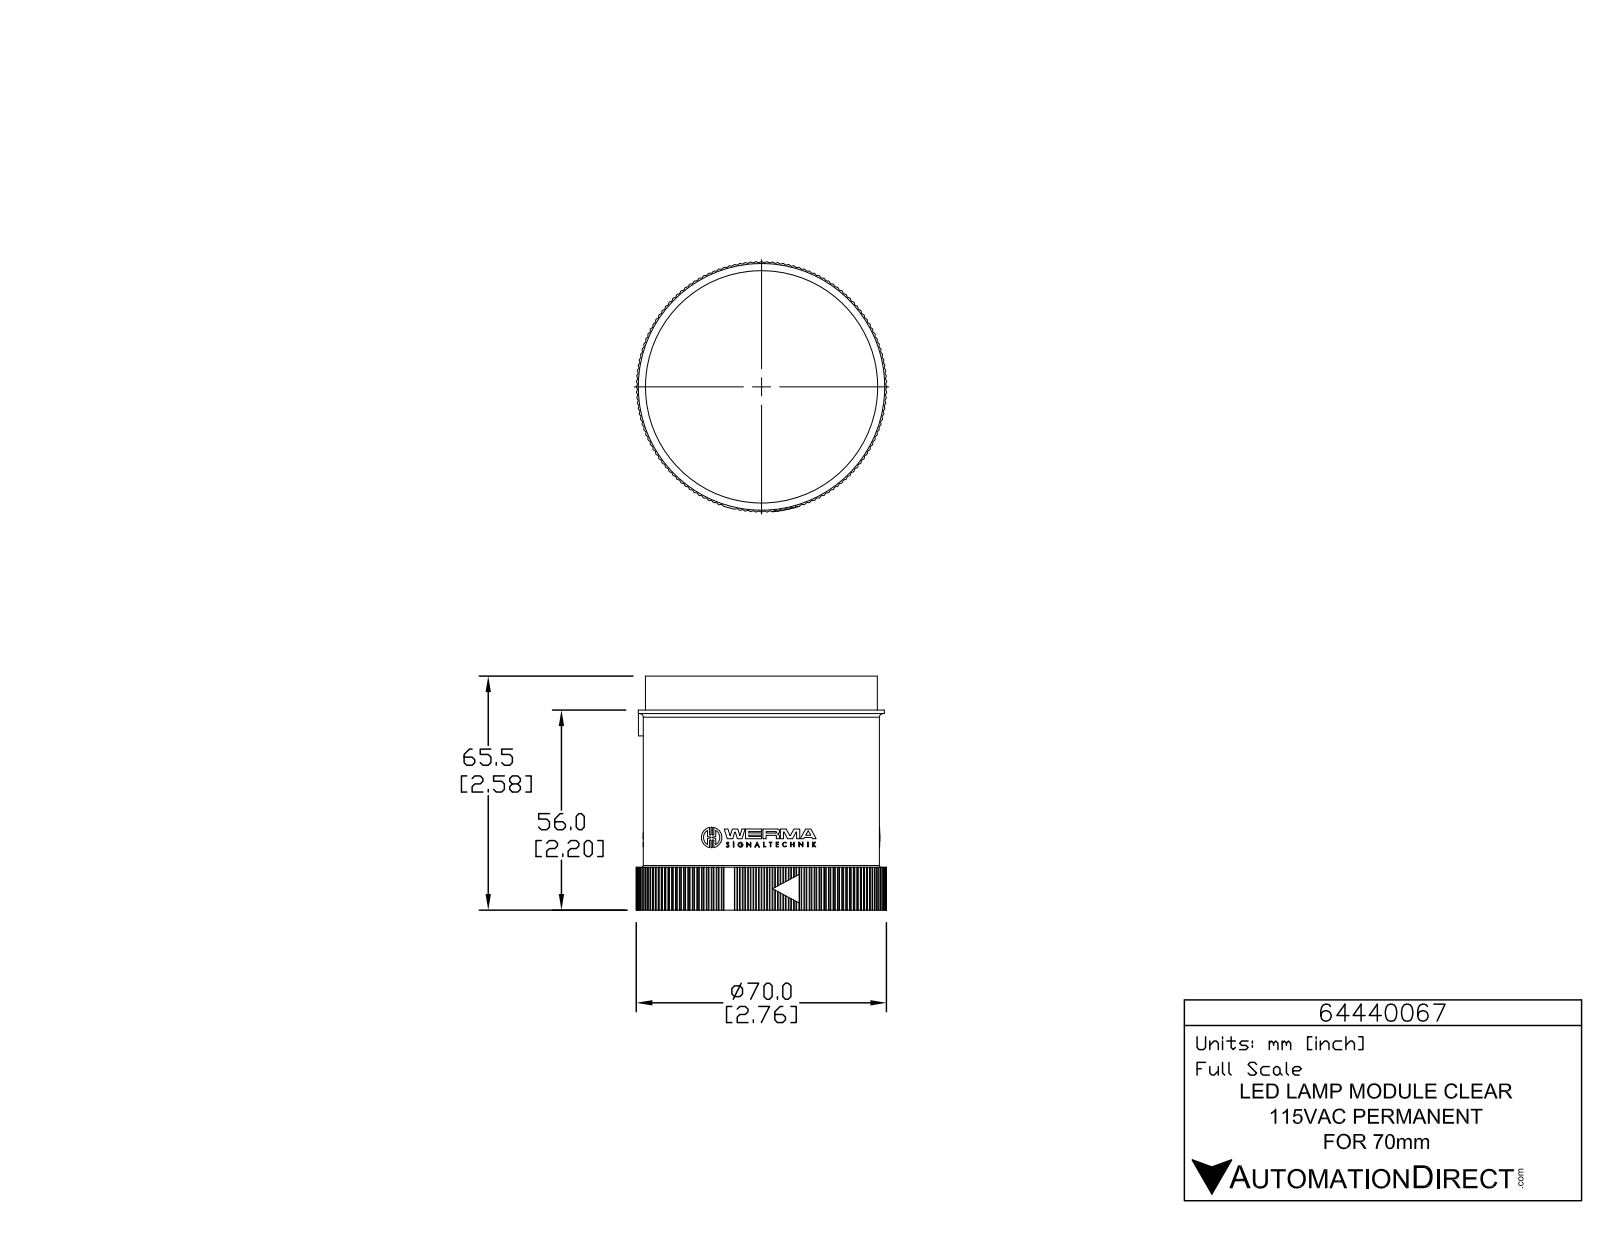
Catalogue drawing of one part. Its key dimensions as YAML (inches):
part_name: "64440067"
step_written_by: "SolidWorks 2015 (AUTOMOTIVE_DESIGN)"
units: inches
bodies: {solids: 1, faces: 1400, planar: 832, cylindrical: 563, other: 5}
overall_size: [2.762, 2.762, 2.579]
volume: 12.02
surface_area: 37.48
round_holes:
  - {diameter: 0.039, count: 3}
  - {diameter: 2.575, count: 1}
round_bosses_or_shafts:
  - {diameter: 0.226, count: 3}
  - {diameter: 0.056, count: 3}
  - {diameter: 2.717, count: 1}
  - {diameter: 2.606, count: 1}
  - {diameter: 2.559, count: 1}
partial_cylinders:
  - {radius: 0.008, count: 285}
  - {radius: 0.008, count: 6}
  - {radius: 0.008, count: 6}
  - {radius: 0.008, count: 6}
  - {radius: 0.131, count: 6}
  - {radius: 0.004, count: 3}
  - {radius: 0.005, count: 3}
  - {radius: 0.008, count: 3}
face_to_face_distances: [2.201, 2.451, 0.378, 2.579, 2.205, 1.827, 0.374, 2.452, 0.472, 0.094]
